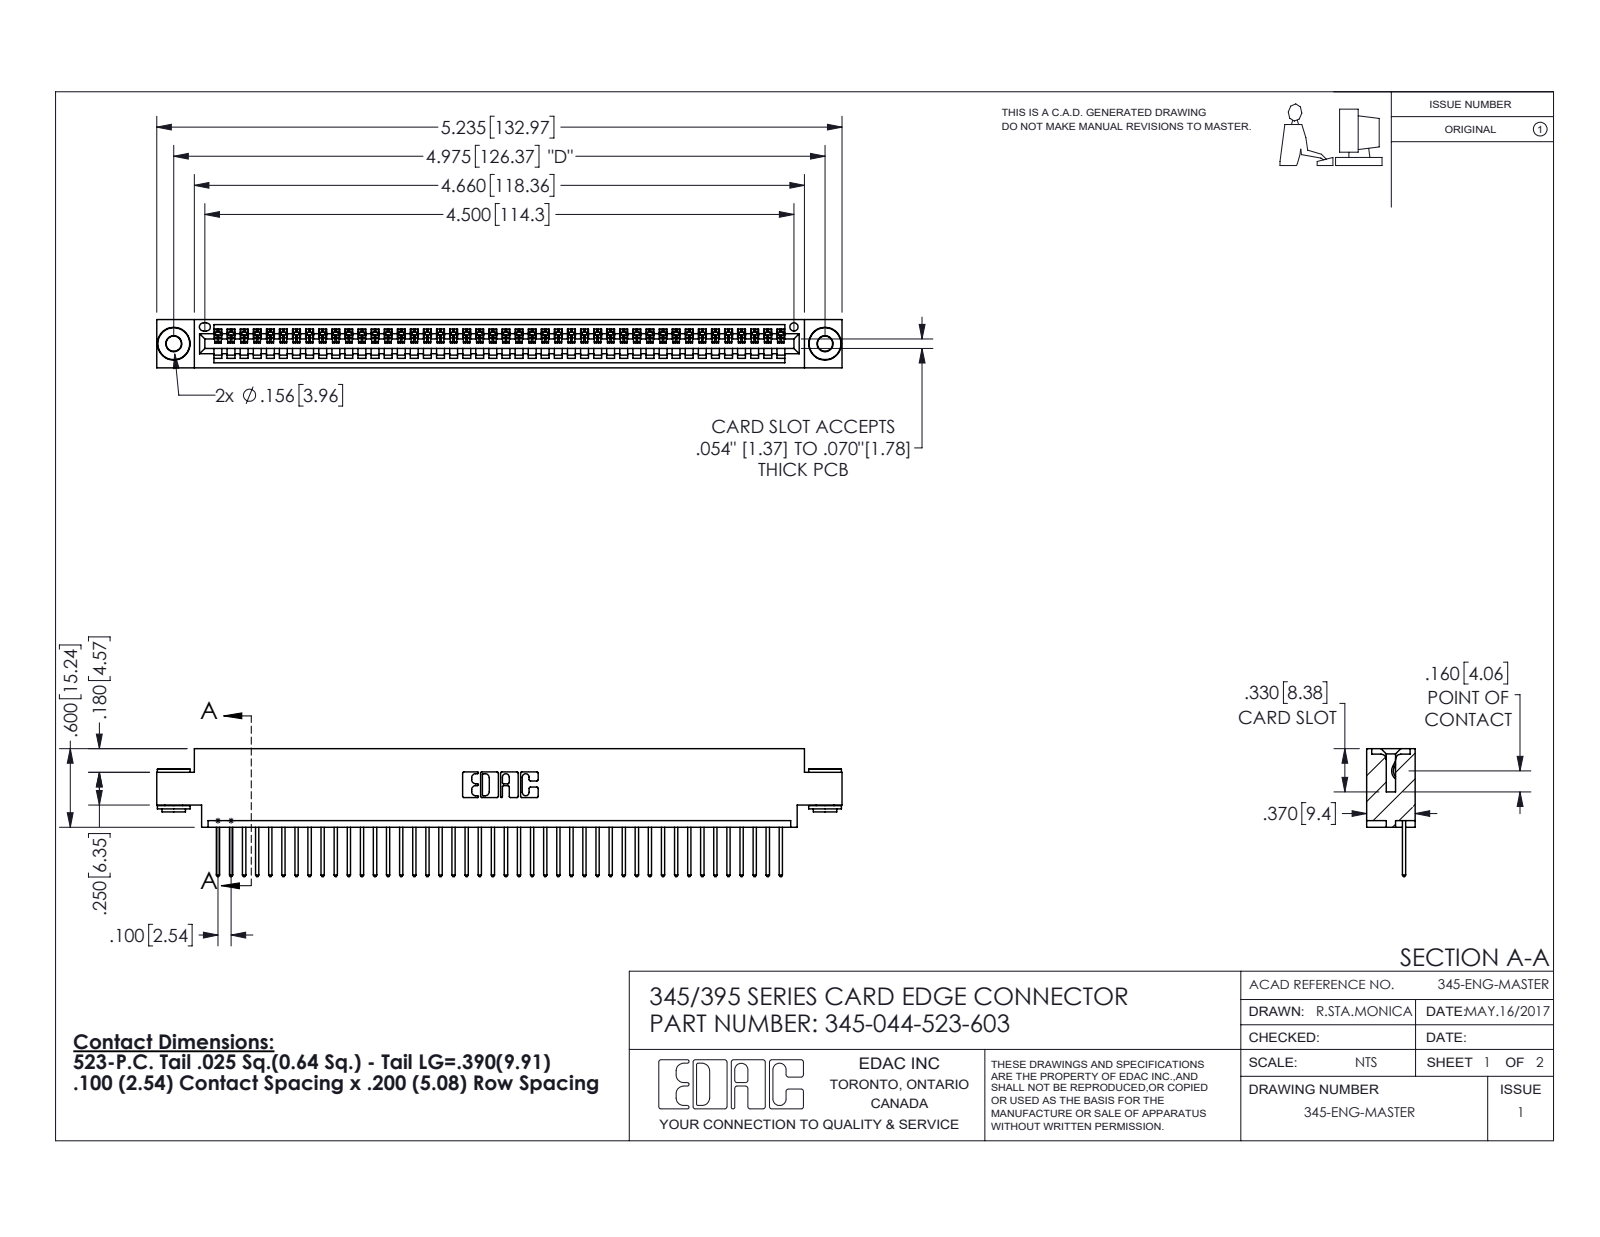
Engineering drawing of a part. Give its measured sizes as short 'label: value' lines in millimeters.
name: 345 Part_0.170 Offset - 0.156 Dia-TH; 345-250-002_345-250-002-102; 345-292-001_345-293-123; 345-044-523-603
written by: SolidWorks 2016 (CONFIG_CONTROL_DESIGN)
unit: mm
bodies: 47 solids, 2720 faces (1854 planar, 858 cylindrical, 8 other)
size: 133 × 24.8 × 9.4
volume: 12 500 mm³; area: 17 070 mm²
holes: 2× ⌀2.9, 2× ⌀4, 1× ⌀1.6
bosses: 2× ⌀6.4, 2× ⌀4.6, 2× ⌀3.5
rounds: 88× R0.2, 88× R0.3, 22× R0.3, 6× R0.2, 6× R0.8, 3× R0.7, 2× R0.8, 2× R1
face distances: 1.8, 7.6, 9.4, 5.1, 2.5, 6.9, 0.6, 5.7, 4.4, 3.8
hole spacings: 6.9, 120.4, 126.4
